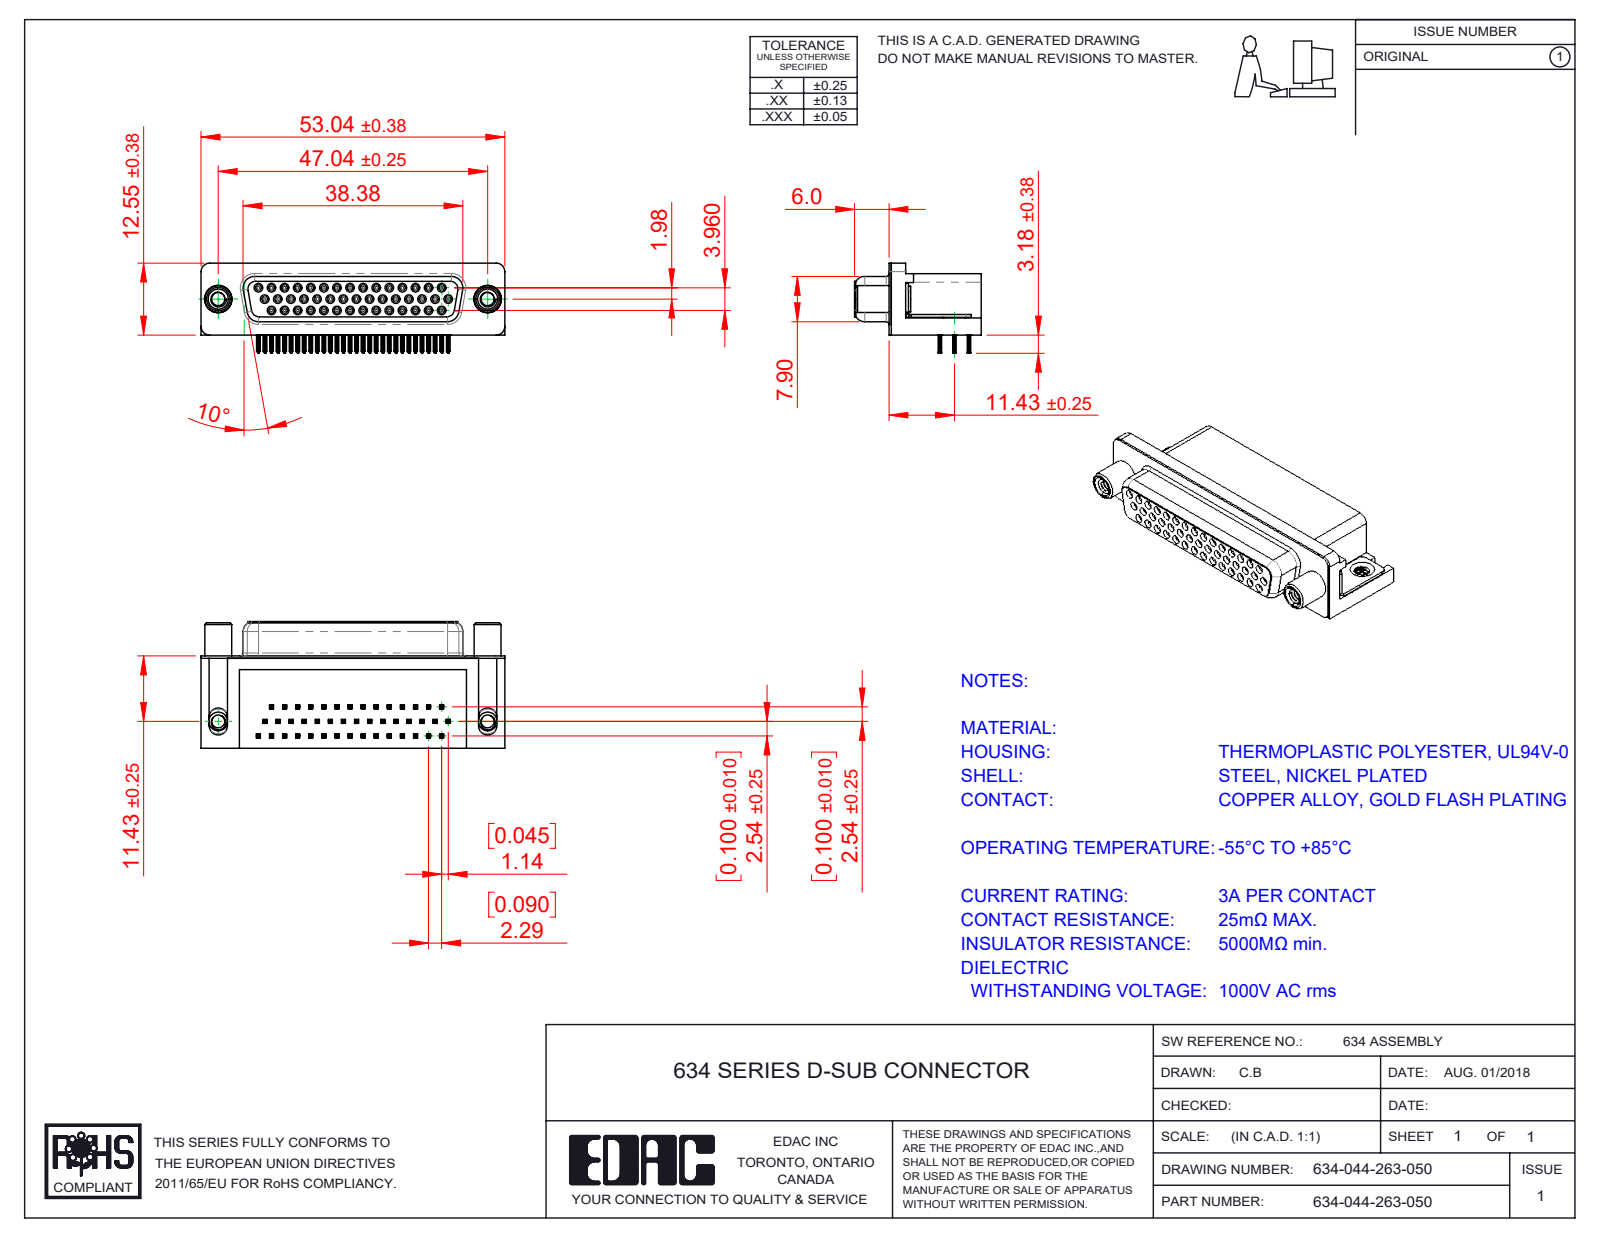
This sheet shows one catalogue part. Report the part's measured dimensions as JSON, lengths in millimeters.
{"part_name": "634-044-263-050; Round Threaded Standoff; 4-40 Threaded Board Mount; 634 Shell_44 Socket (+4 more)", "step_written_by": "SolidWorks 2016 (CONFIG_CONTROL_DESIGN)", "units": "millimeters", "bodies": {"solids": 50, "faces": 6561, "planar": 2921, "cylindrical": 1516, "other": 2124}, "overall_size": [53.04, 22.1, 15.73], "volume_mm3": 9459, "surface_area_mm2": 13559, "round_holes": [[0.8, 44], [0.9, 44], [2.26, 2], [2.3, 2], [3.1, 2], [4, 2], [4.8, 2], [5, 2]], "round_bosses_or_shafts": [[1.2, 44], [4.9, 2], [4.7, 2], [4.5, 2], [3.85, 2], [3.26, 2]], "partial_cylinders_radius": [[0.1, 352], [0.15, 176], [0.35, 88], [0.34, 44], [1, 19], [0.28, 14], [1.35, 8], [1.6, 8]], "face_to_face_distances": [0.4, 10.35, 15.7, 9.03, 0.35, 1.98, 0.85, 6.65, 0.6, 7.05], "hole_center_spacings": [4.57, 2.29, 4.58, 12.1, 2.27, 3.96, 6.05, 2.28]}
